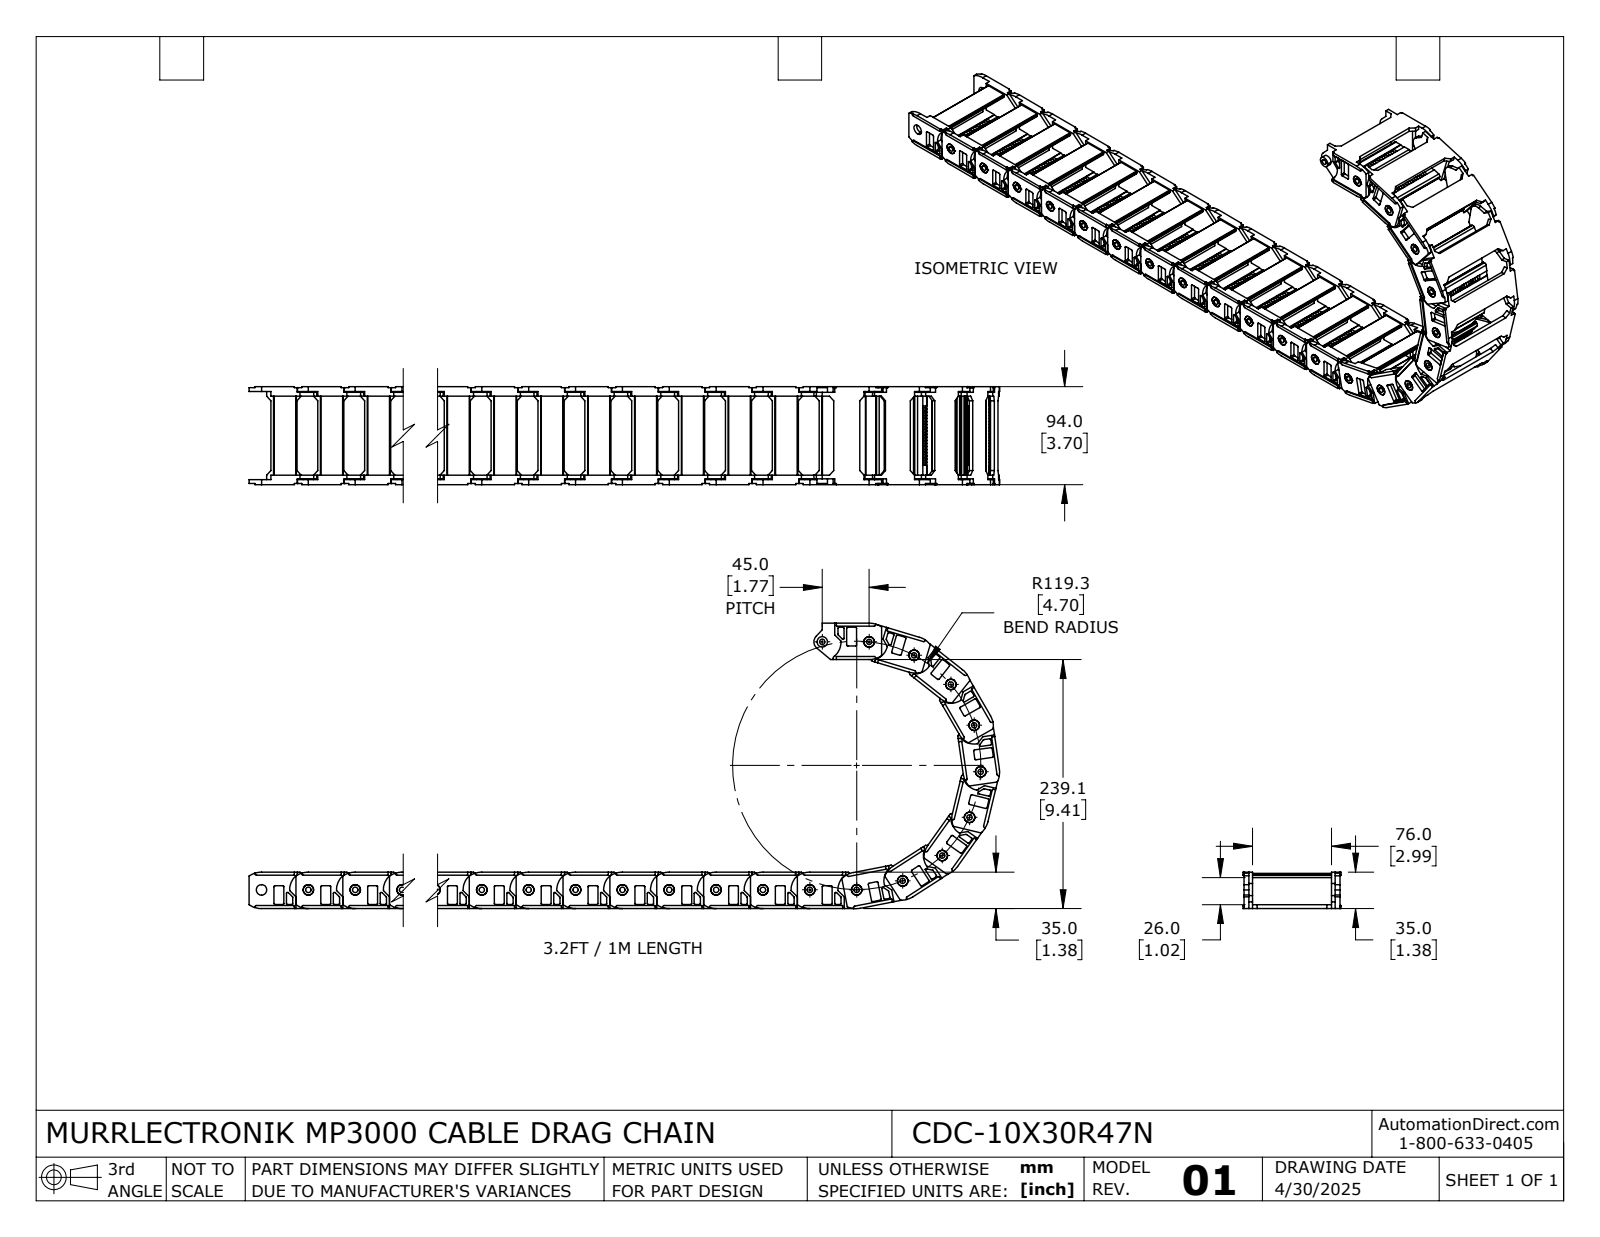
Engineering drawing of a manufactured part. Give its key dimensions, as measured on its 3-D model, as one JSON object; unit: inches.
{"part_name": "CDC-10X30R47N", "step_written_by": "SolidWorks 2024 (AUTOMOTIVE_DESIGN)", "units": "inches", "bodies": {"solids": 22, "faces": 4752, "planar": 3652, "cylindrical": 1100, "other": 0}, "overall_size": [28.908, 10.792, 3.701], "volume_in3": 44.66, "surface_area_in2": 695.2, "round_holes": [[0.201, 22], [0.398, 22]], "round_bosses_or_shafts": [[0.394, 22]], "partial_cylinders_radius": [[0.039, 176], [0.02, 88], [0.059, 44], [0.079, 44], [0.827, 44], [0.11, 22], [0.315, 22], [0.709, 22]], "face_to_face_distances": [3.307, 0.315, 0.157, 1.181, 0.146, 3.476, 0.169, 3.161, 0.138, 2.992], "hole_center_spacings": [1.772, 3.543, 5.315, 7.087, 8.858, 10.63, 12.402, 6.473]}
